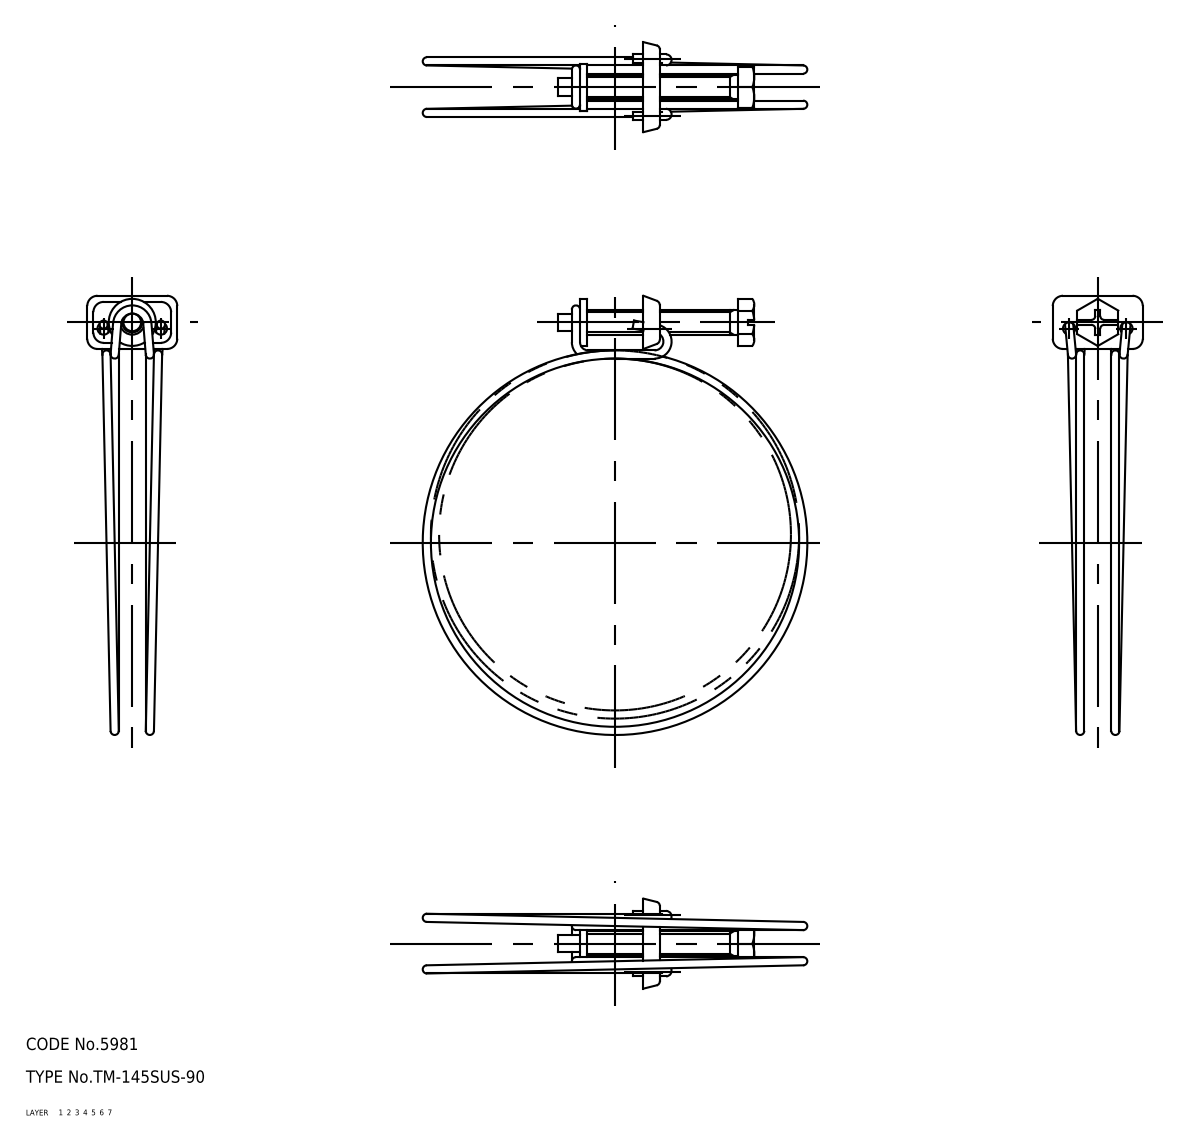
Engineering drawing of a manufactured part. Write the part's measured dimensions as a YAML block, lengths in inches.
part_name: "screw; holder; band; TM_145SUS_90_23078_36"
step_written_by: "CADfix (AUTOMOTIVE_DESIGN)"
units: inches
bodies: {solids: 3, faces: 119, planar: 0, cylindrical: 0, other: 119}
overall_size: [4.226, 3.701, 0.866]
volume: 0.257
surface_area: 9.853
